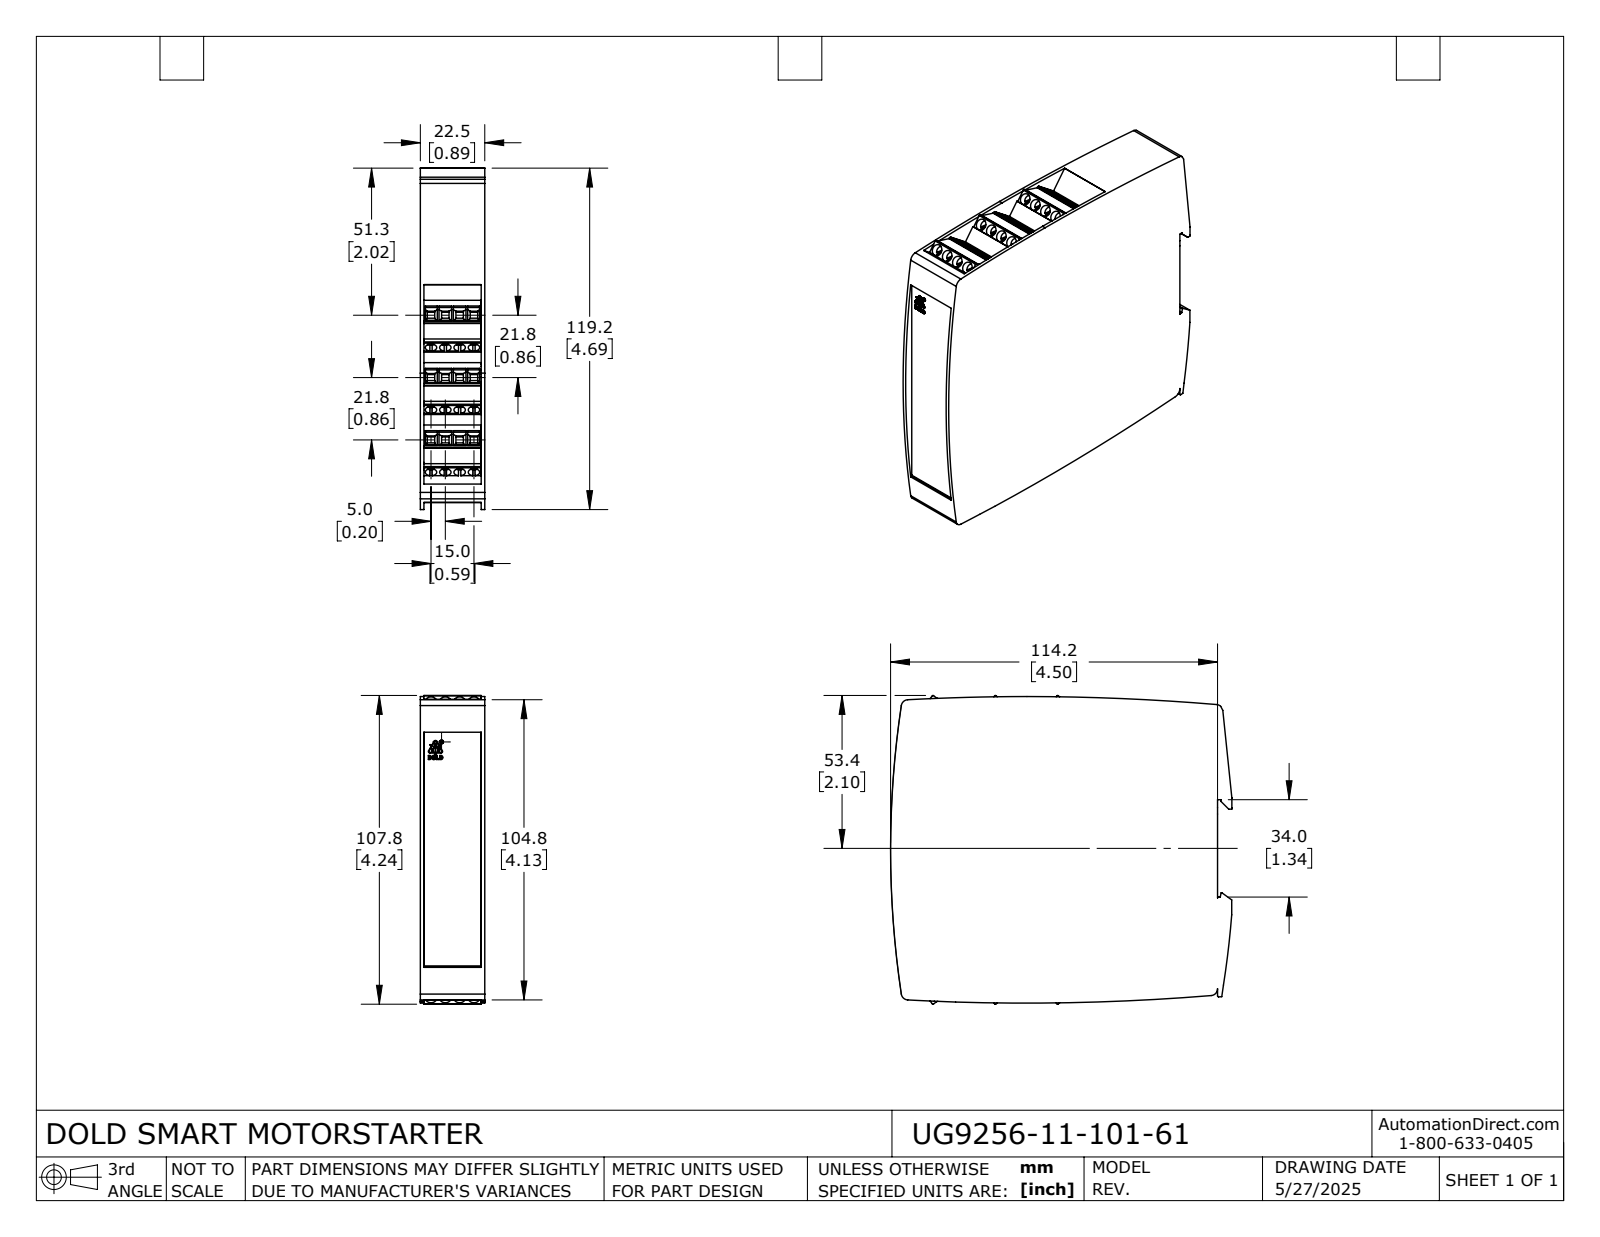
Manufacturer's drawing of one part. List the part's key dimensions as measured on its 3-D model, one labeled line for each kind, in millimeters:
Part name (STEP PRODUCT): UG9256-11-101-61
STEP written by: SolidWorks 2024 (AUTOMOTIVE_DESIGN)
Units: millimetres
Bodies: 1 solid, 1036 faces (813 planar, 222 cylindrical, 1 other)
Overall size (bounding box): 119.2 × 107.8 × 22.5
Volume: 259 700 mm³ · Surface area: 41 750 mm²
Round holes (diameter × count): ⌀4 ×24, ⌀1.3 ×1
Round bosses / shafts (diameter × count): ⌀3.8 ×24, ⌀1.2 ×1
Partial cylindrical surfaces — rounded edges, fillets, slot ends (radius × count): R0.3 ×15, R0.5 ×14, R0.1 ×12, R2.4 ×7, R0.1 ×6, R0.1 ×4, R800 ×4, R0.5 ×3
Main face-to-face distances: 22.5, 1.2, 21.3, 17.1, 111.2, 1.3, 21.2, 34.3, 13.4, 19.9
Hole centre spacings: 14.3, 5, 13.4, 16.7, 10, 27.3, 20.1, 26.8
